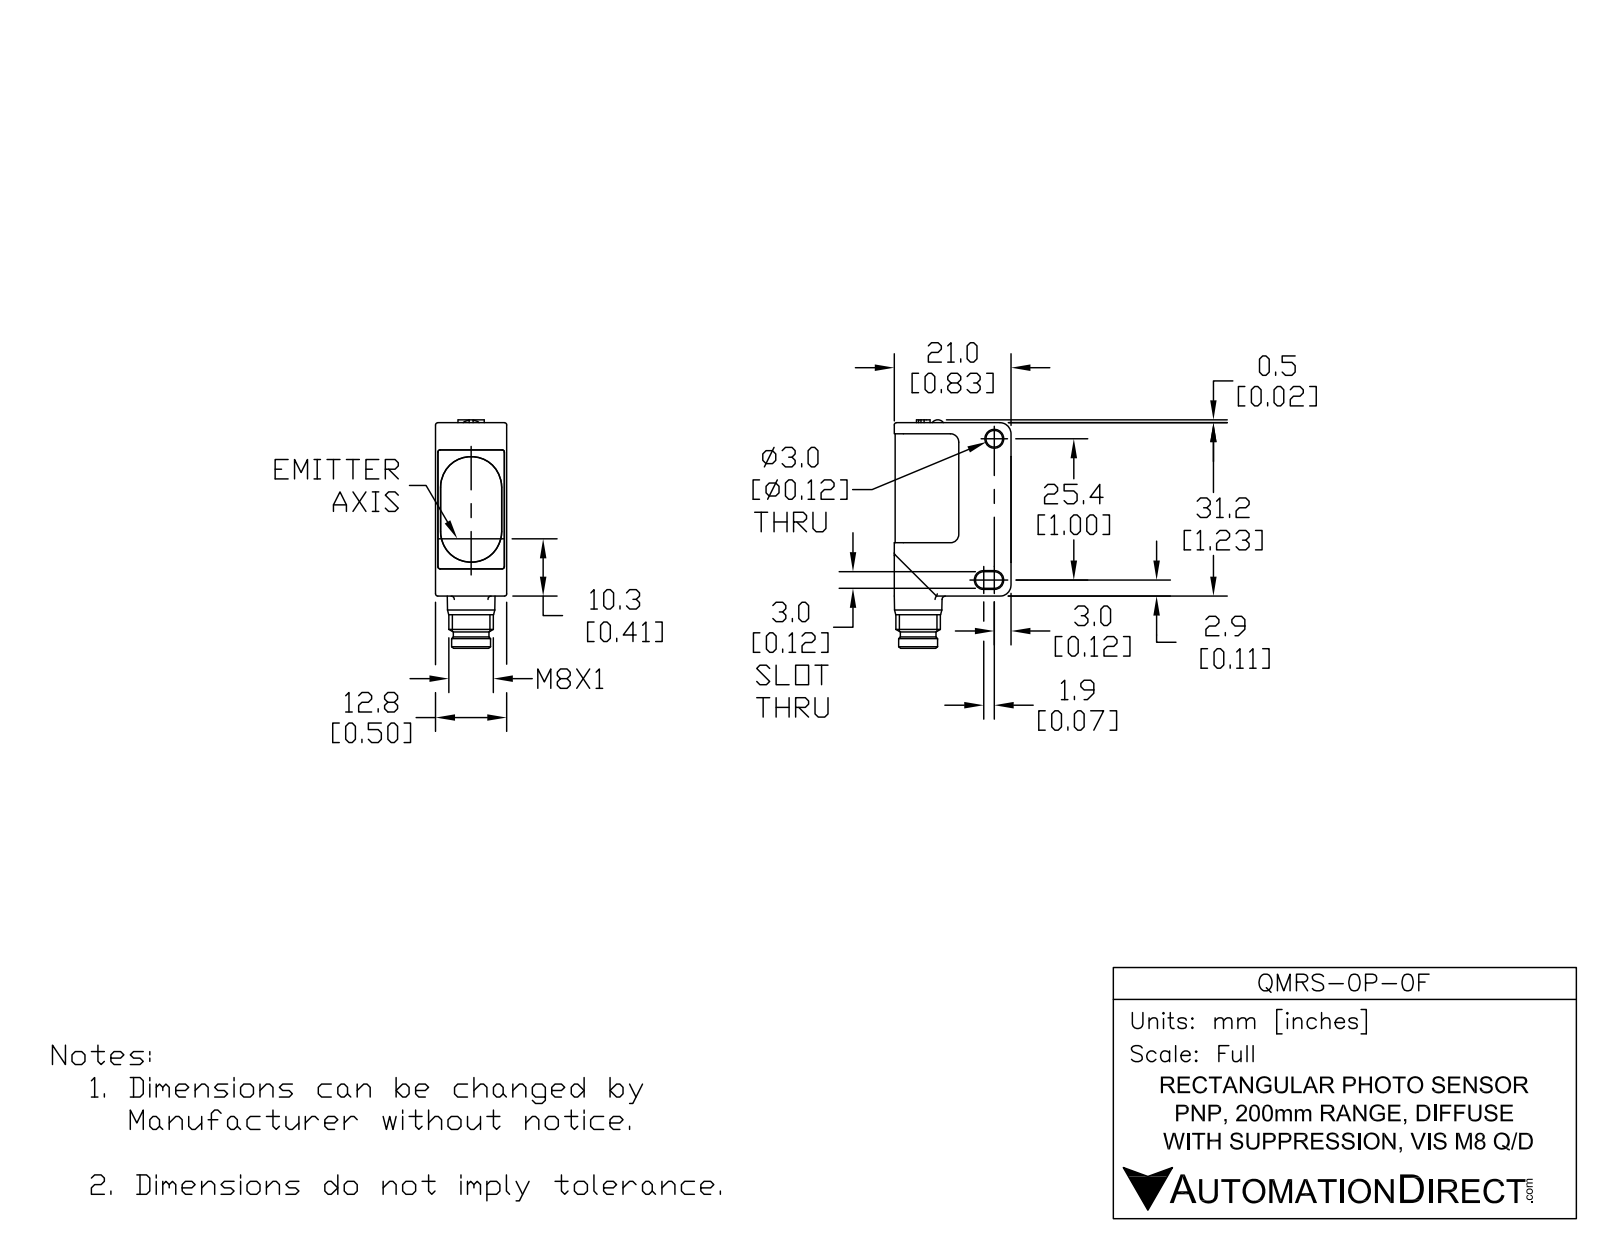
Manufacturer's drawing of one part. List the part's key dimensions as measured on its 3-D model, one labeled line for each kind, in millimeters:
Part name (STEP PRODUCT): QMRS-0P-0F
STEP written by: SolidWorks 2017 (AUTOMOTIVE_DESIGN)
Units: millimetres
Bodies: 7 solids, 262 faces (123 planar, 92 cylindrical, 47 other)
Overall size (bounding box): 41.1 × 21 × 12.8
Volume: 7 670 mm³ · Surface area: 4 981 mm²
Round holes (diameter × count): ⌀3 ×1, ⌀4.4 ×1, ⌀5.8 ×1
Round bosses / shafts (diameter × count): ⌀1 ×4, ⌀8 ×1, ⌀7 ×1, ⌀6.4 ×1, ⌀3.1 ×1, ⌀2.8 ×1
Partial cylindrical surfaces — rounded edges, fillets, slot ends (radius × count): R0.4 ×10, R1.5 ×7, R0.6 ×4, R1 ×4, R4.5 ×4, R0.5 ×3, R1.7 ×2, R2 ×2
Main face-to-face distances: 12.6, 12.8, 0.5, 2.8, 1, 0.4, 1.8, 12.5, 12.4, 12.2
Hole centre spacings: 7.9
